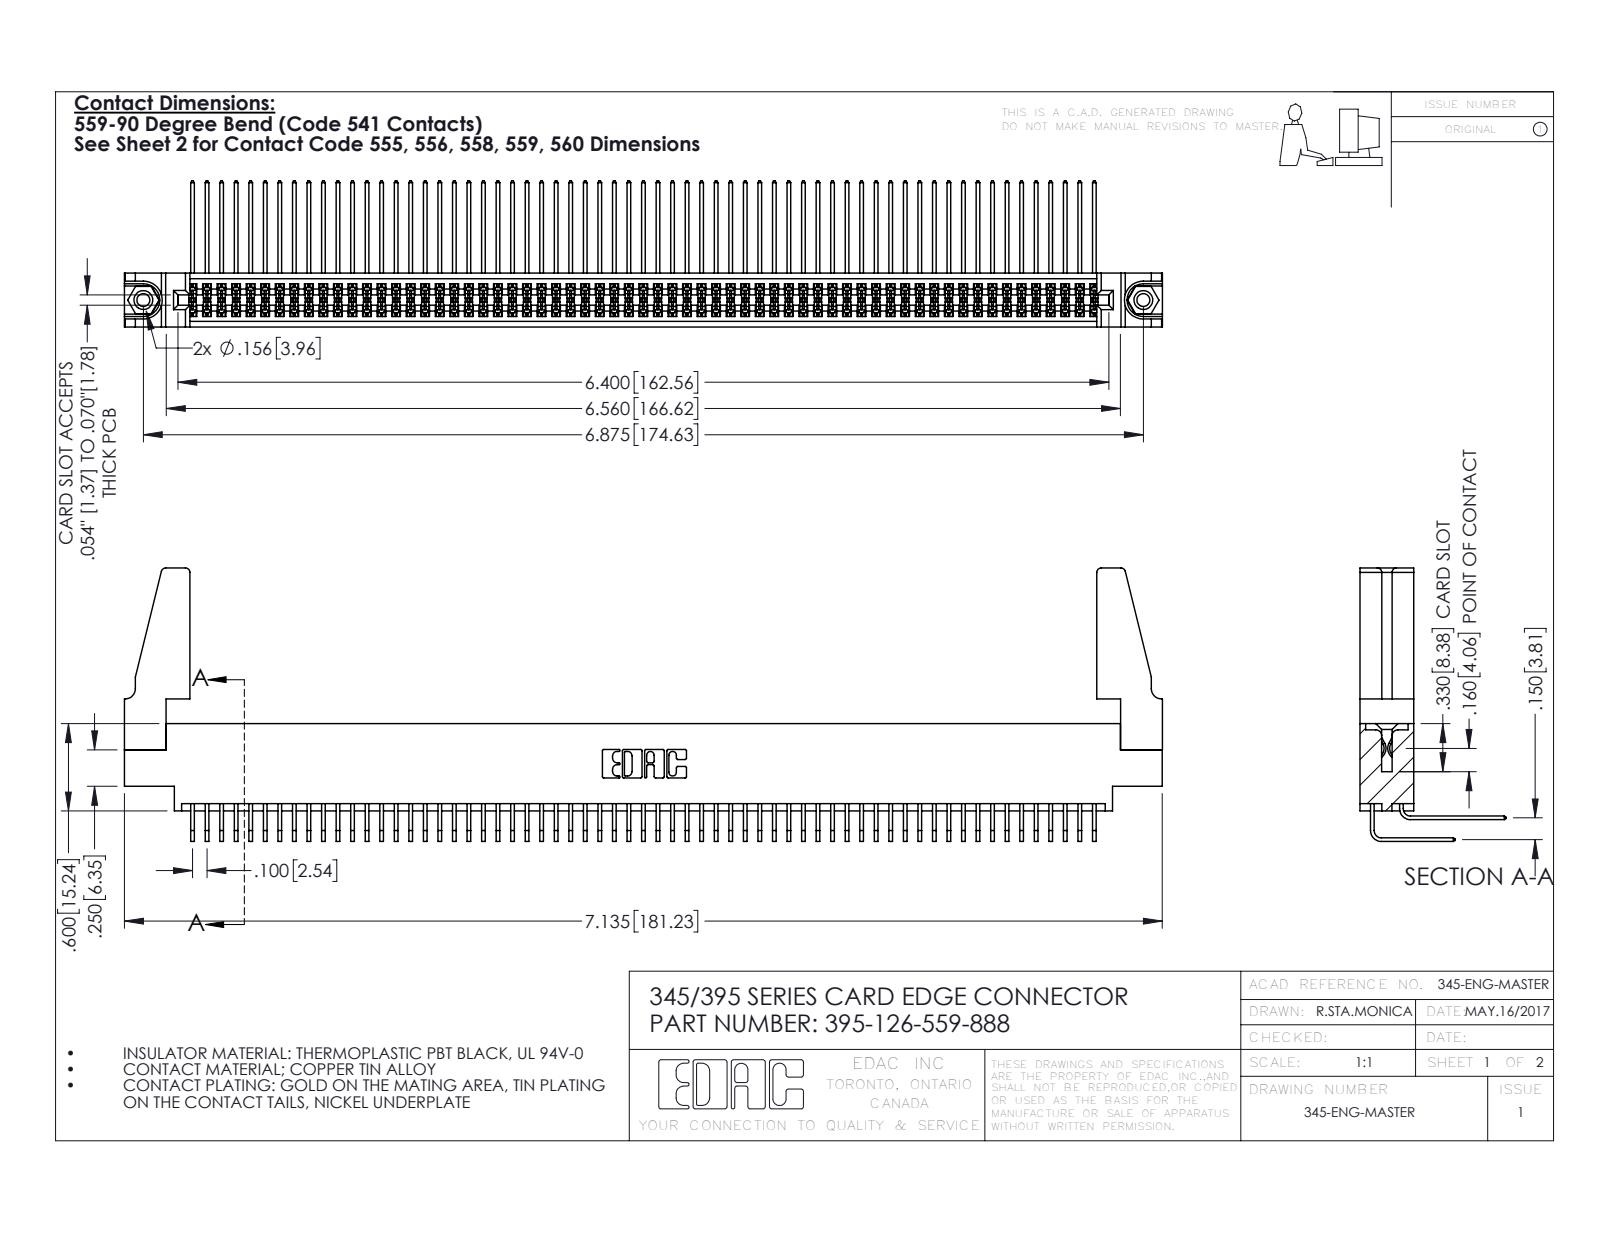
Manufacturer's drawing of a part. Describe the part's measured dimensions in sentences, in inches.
The part is named "345-292-001_559 Tail - 2; 345-220-078_345-220-088; 395-126-559-888; 345-250-001_345-250-001-102 (+2 more)". Its 3-D file was written by "SolidWorks 2016 (CONFIG_CONTROL_DESIGN)". It is 131 solids with 6806 faces: 4566 planar, 2224 cylindrical and 16 other. Overall it measures 7.136 by 1.879 by 1.005 inches. Its volume is 1.322 cubic inches and its surface area 53.18 square inches. Round holes: 2 of diameter 0.089, 2 of diameter 0.125, 2 of diameter 0.156, 1 of diameter 0.064. Round bosses or shafts: 2 of diameter 0.155. Partial cylindrical surfaces (rounded edges, fillets, slot ends): 189 of radius 0.006, 22 of radius 0.01, 8 of radius 0.03, 6 of radius 0.007, 6 of radius 0.031, 3 of radius 0.026, 2 of radius 0.014, 2 of radius 0.019. The main face-to-face distances are 0.072, 0.298, 0.37, 0.2, 0.098, 0.272, 0.025, 0.225, 0.15, 0.175. The hole center spacings are 0.27, 6.639, 6.875.
